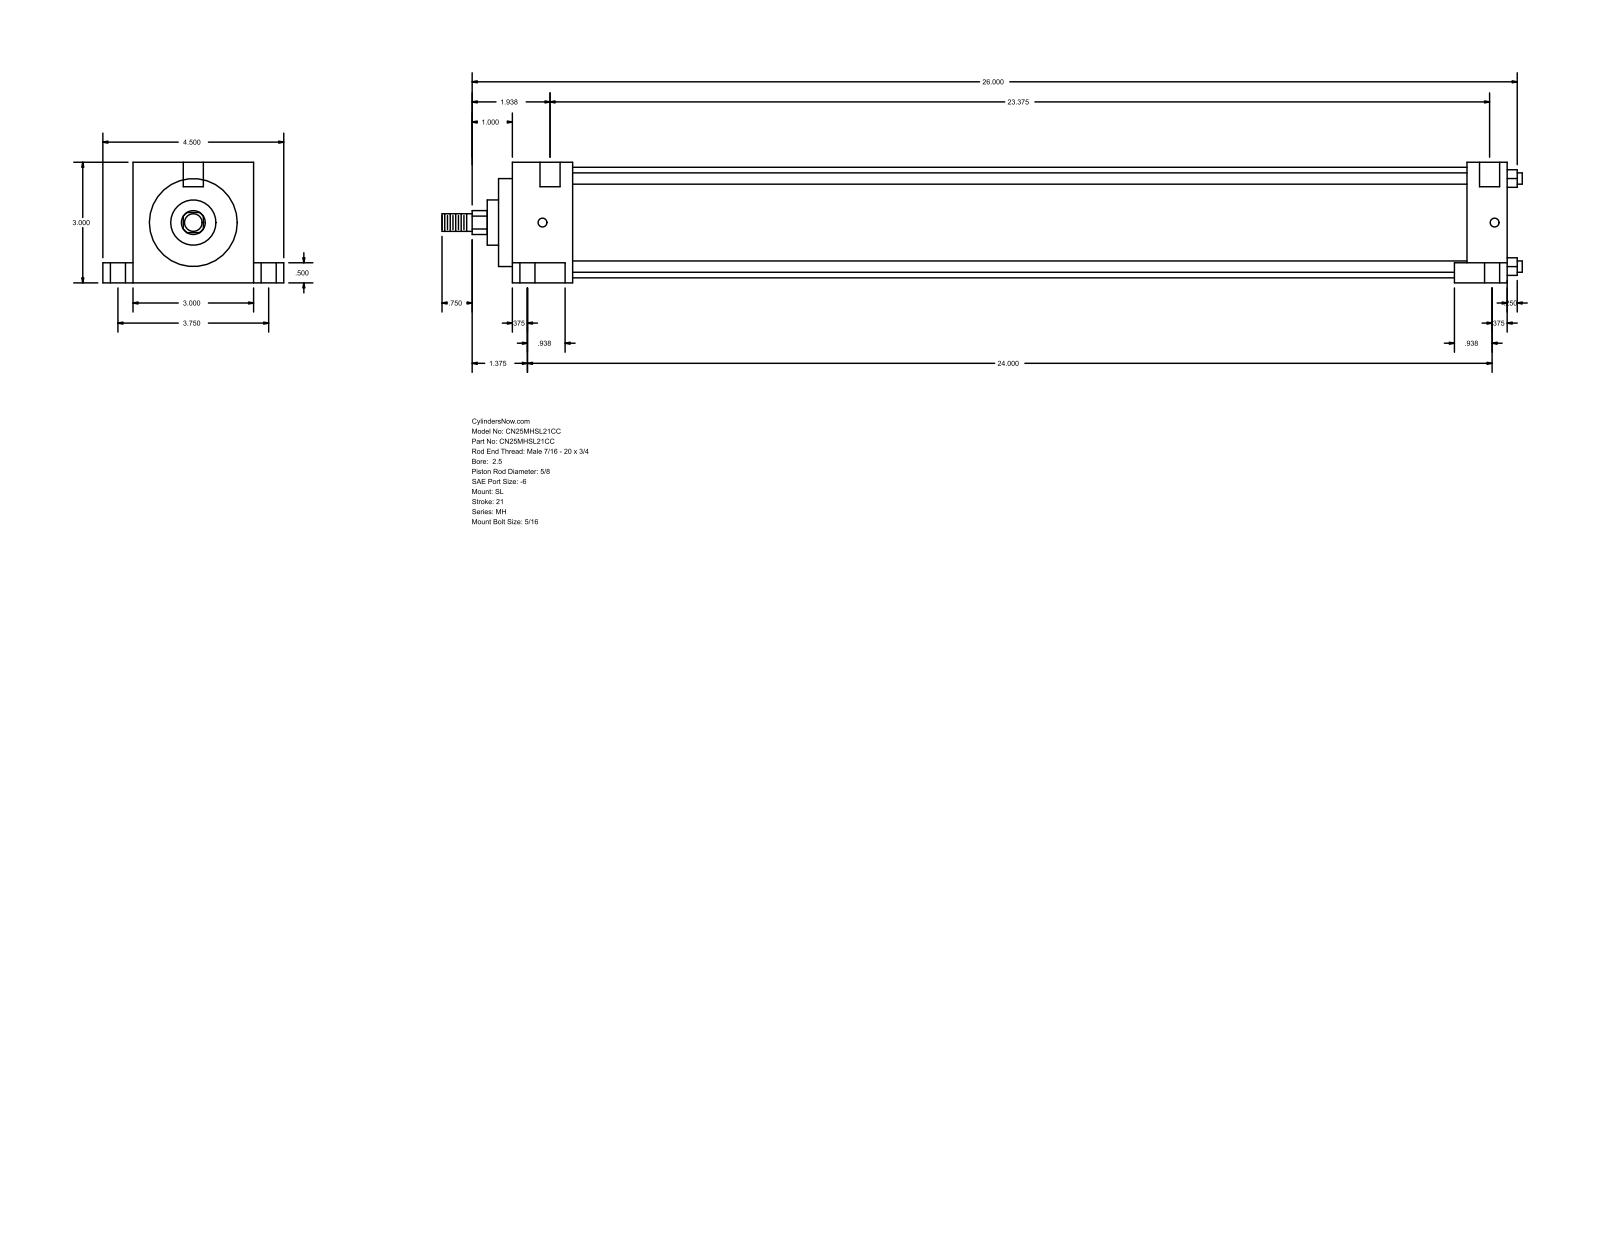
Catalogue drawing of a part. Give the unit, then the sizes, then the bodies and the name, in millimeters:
Units: millimetres
Overall size (bounding box): 682.62 × 114.3 × 76.2
Round holes (diameter × count): ⌀5.56 ×2, ⌀9.53 ×2, ⌀15.88 ×2, ⌀12.7 ×1
Round bosses / shafts (diameter × count): ⌀7.14 ×4, ⌀69.85 ×1, ⌀55.55 ×1, ⌀28.57 ×1, ⌀15.88 ×1, ⌀11.11 ×1
Partial cylindrical surfaces — rounded edges, fillets, slot ends (radius × count): R7.54 ×1
Main face-to-face distances: 76.2, 25.4, 611.98, 637.38, 63.5, 12.7, 19.05, 95.25, 31.75, 604.04
Hole centre spacings: 47.65, 3.17, 95.24
Bodies: 0 solids, 86 faces (61 planar, 25 cylindrical, 0 other)
Part name (STEP PRODUCT): MH_SL__0250_0.625
STEP written by: GSSL Pune (CONFIG_CONTROL_DESIGN)
